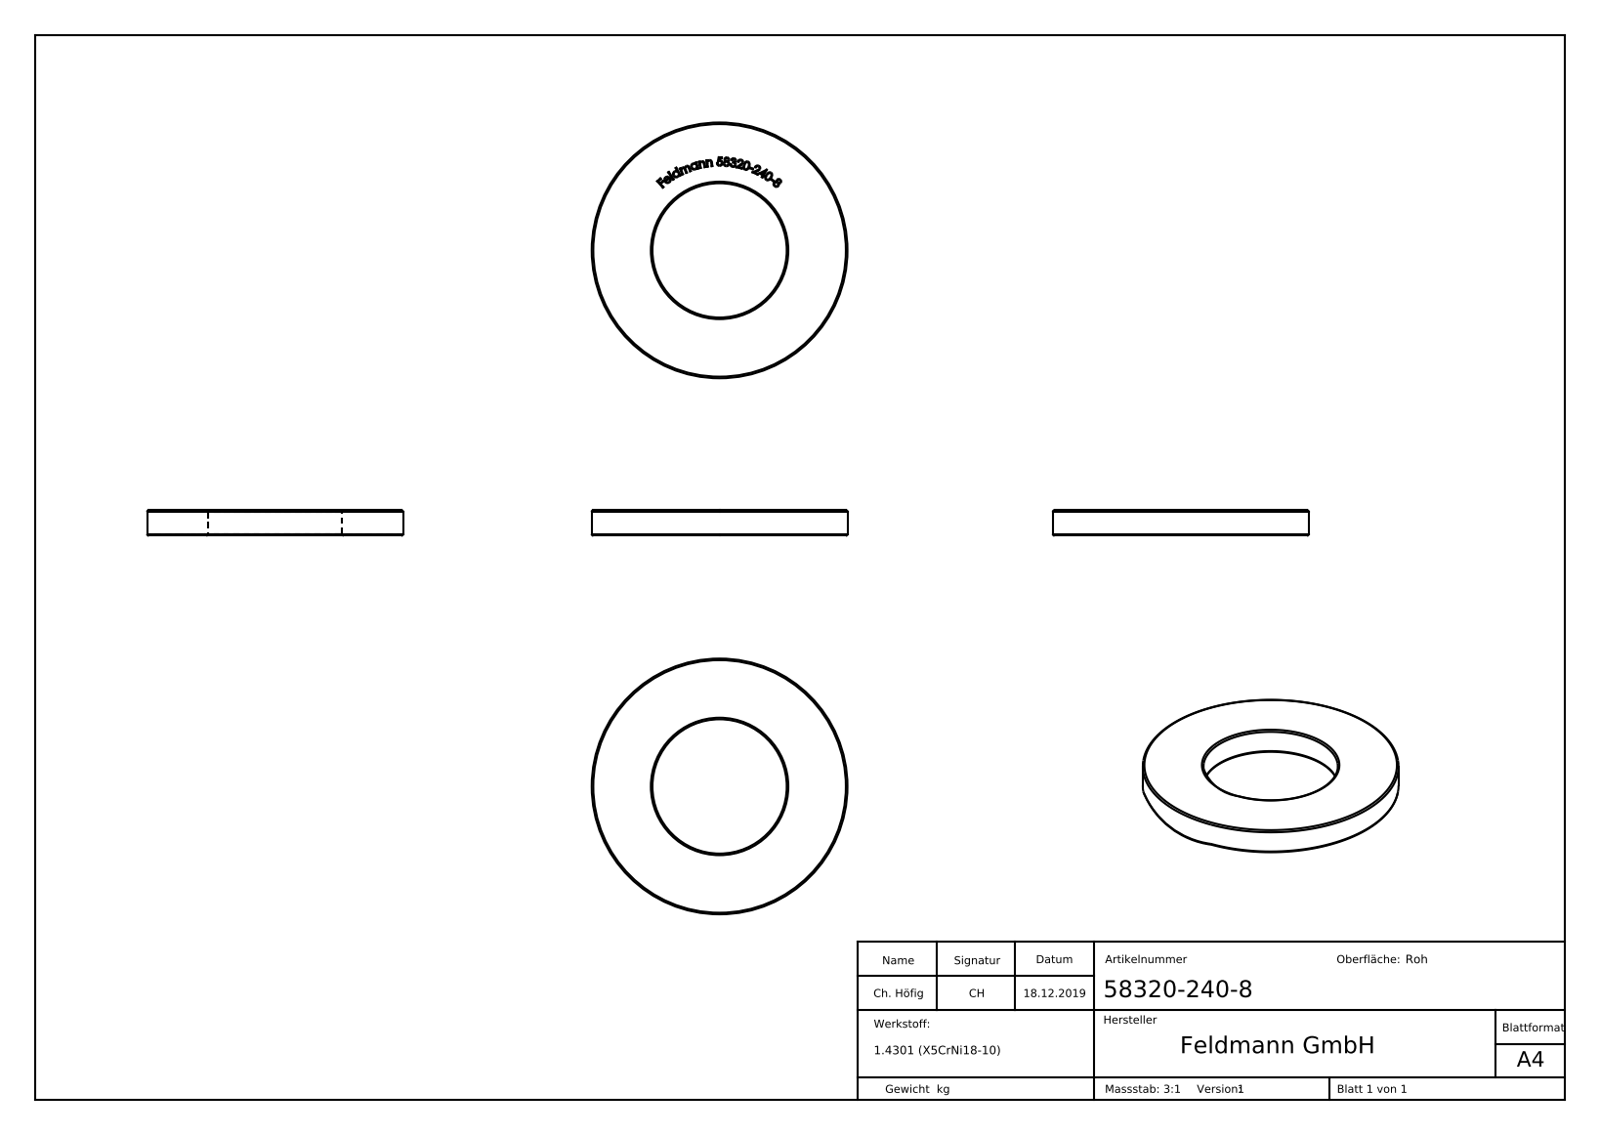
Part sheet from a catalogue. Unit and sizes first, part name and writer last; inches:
Units: inches
Overall size (bounding box): 0.63 × 0.63 × 0.063
Round holes (diameter × count): ⌀0.331 ×1
Round bosses / shafts (diameter × count): ⌀0.63 ×1
Main face-to-face distances: 0.063, 0.059, 0.013, 0.012, 0.015, 0.021, 0.014, 0.016
Volume: 0.014 in³ · Surface area: 0.639 in²
Bodies: 1 solid, 267 faces (127 planar, 2 cylindrical, 138 other)
Part name (STEP PRODUCT): 58320-240-8
STEP written by: SolidWorks 2015 (CONFIG_CONTROL_DESIGN)
